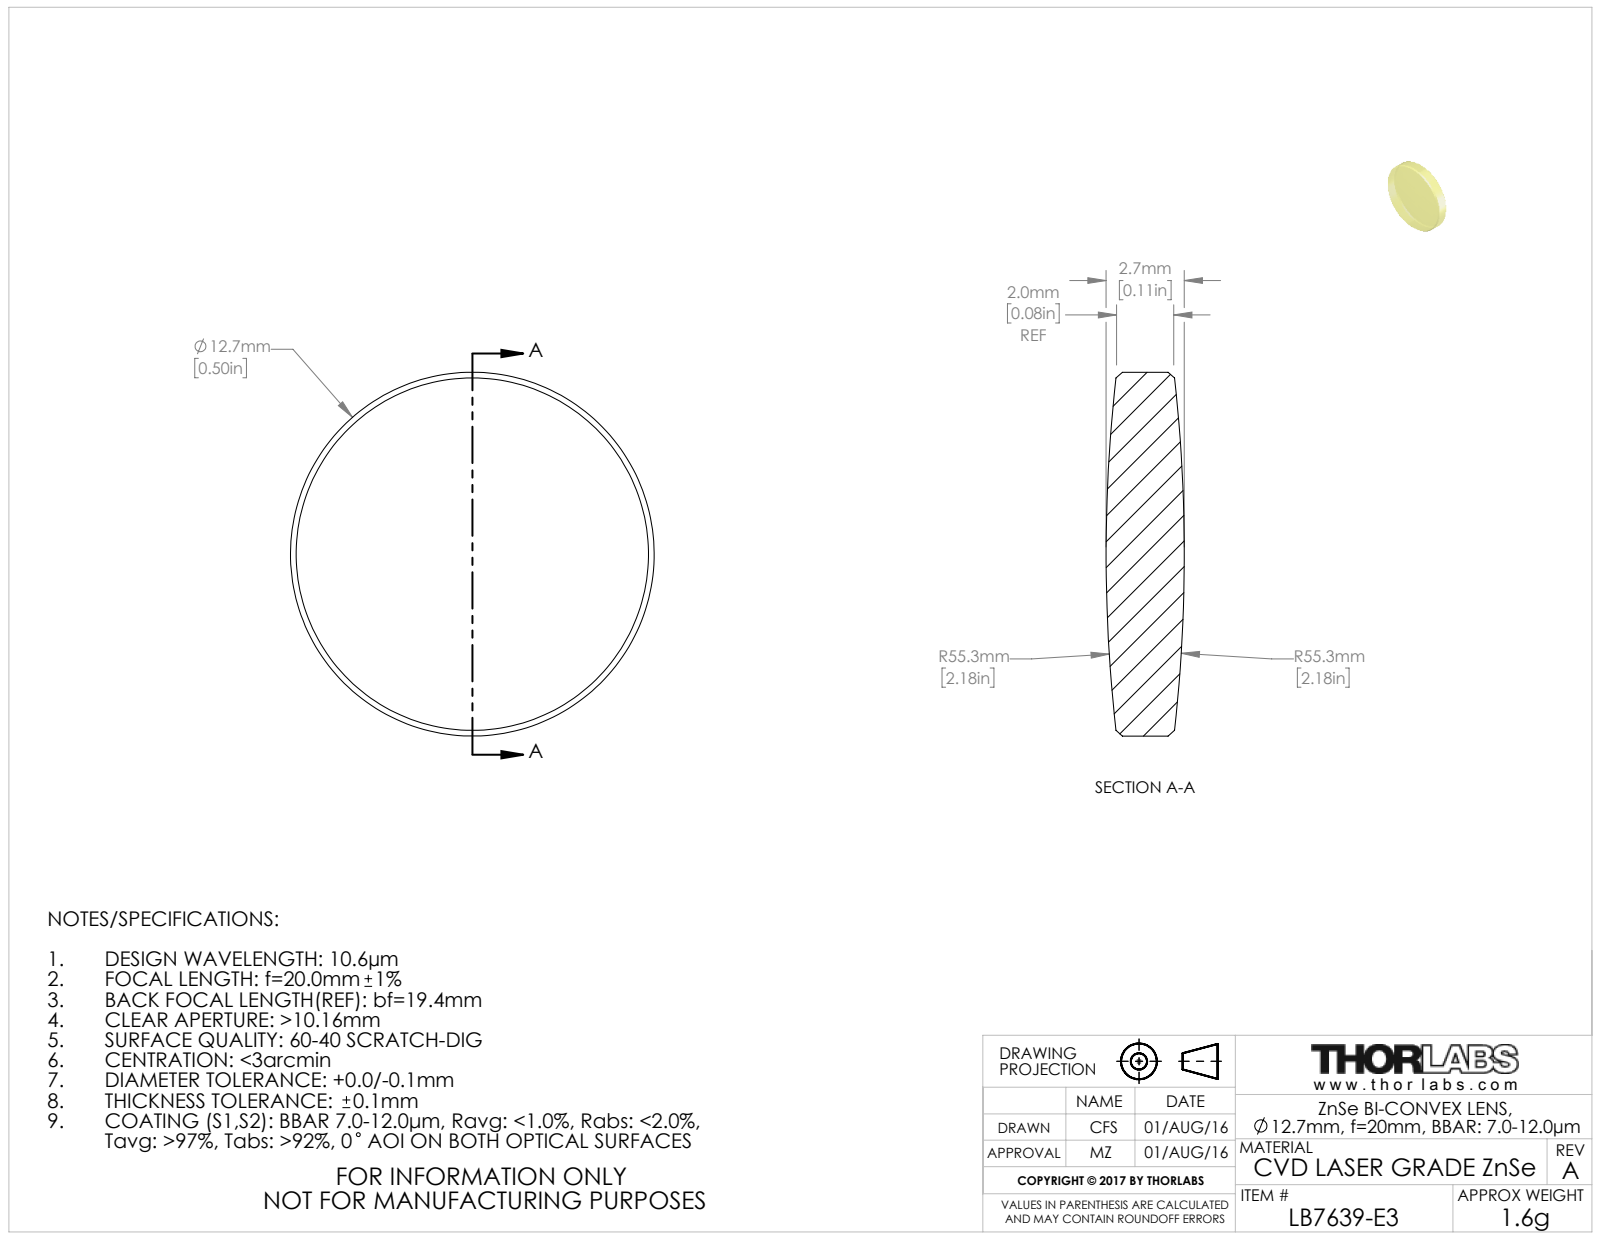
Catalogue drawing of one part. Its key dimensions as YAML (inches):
part_name: "TTN051878-E0W"
step_written_by: "SolidWorks 2016 (CONFIG_CONTROL_DESIGN)"
units: inches
bodies: {solids: 1, faces: 10, planar: 0, cylindrical: 2, other: 8}
overall_size: [0.5, 0.5, 0.107]
volume: 0.018
surface_area: 0.505
round_bosses_or_shafts:
  - {diameter: 0.5, count: 1}
